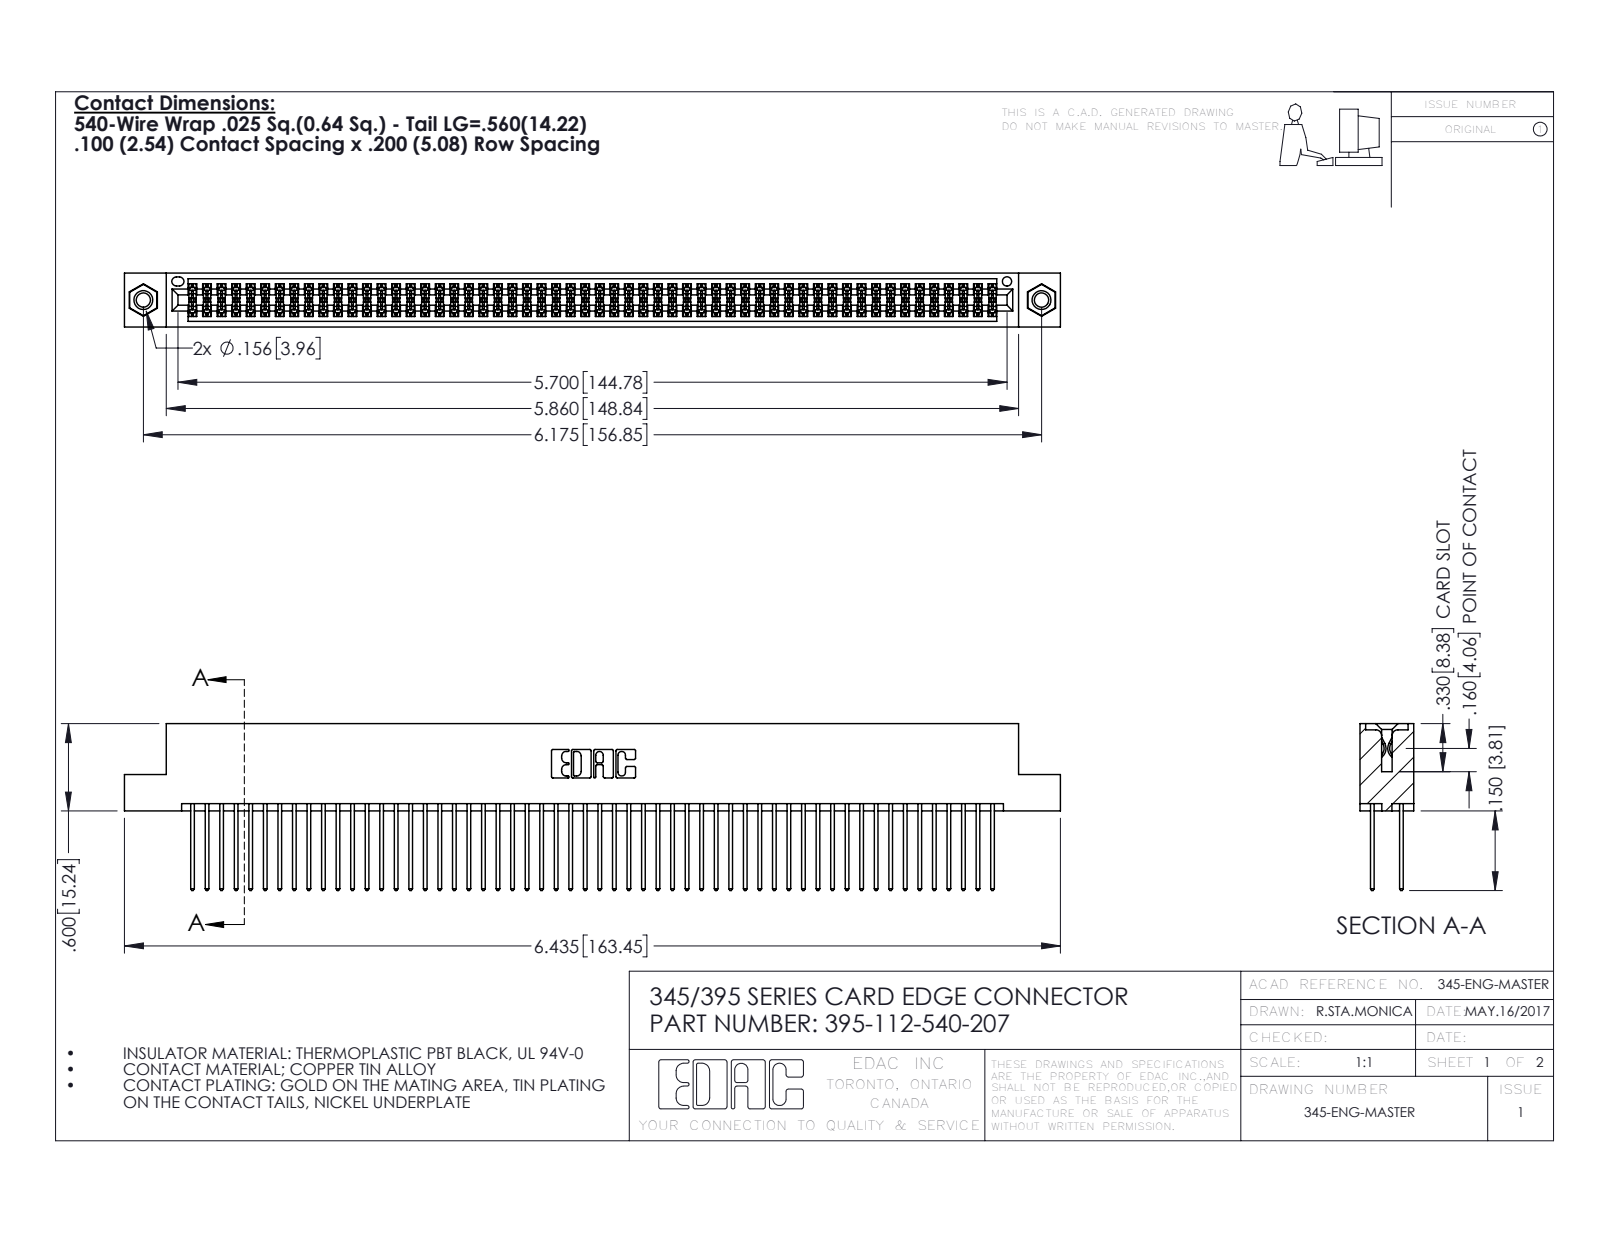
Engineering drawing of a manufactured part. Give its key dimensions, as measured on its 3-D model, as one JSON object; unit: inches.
{"part_name": "395-112-540-207; 345 Part_Flush Mounting Lugs - 0.156 Dia-TI; 345-250-001_345-250-005-103; 345-292-001_345-293-140", "step_written_by": "SolidWorks 2016 (CONFIG_CONTROL_DESIGN)", "units": "inches", "bodies": {"solids": 115, "faces": 5786, "planar": 3808, "cylindrical": 1962, "other": 16}, "overall_size": [6.435, 1.147, 0.37], "volume_in3": 1.002, "surface_area_in2": 41.13, "round_holes": [[0.098, 2], [0.125, 2], [0.156, 2], [0.064, 1]], "round_bosses_or_shafts": [[0.155, 2]], "partial_cylinders_radius": [[0.006, 168], [0.01, 112], [0.01, 22], [0.007, 6], [0.031, 6], [0.026, 3], [0.014, 2], [0.019, 2]], "face_to_face_distances": [0.072, 0.298, 0.2, 0.098, 0.272, 0.025, 0.37, 0.225, 0.175, 0.149], "hole_center_spacings": [0.27, 5.939, 6.175]}
